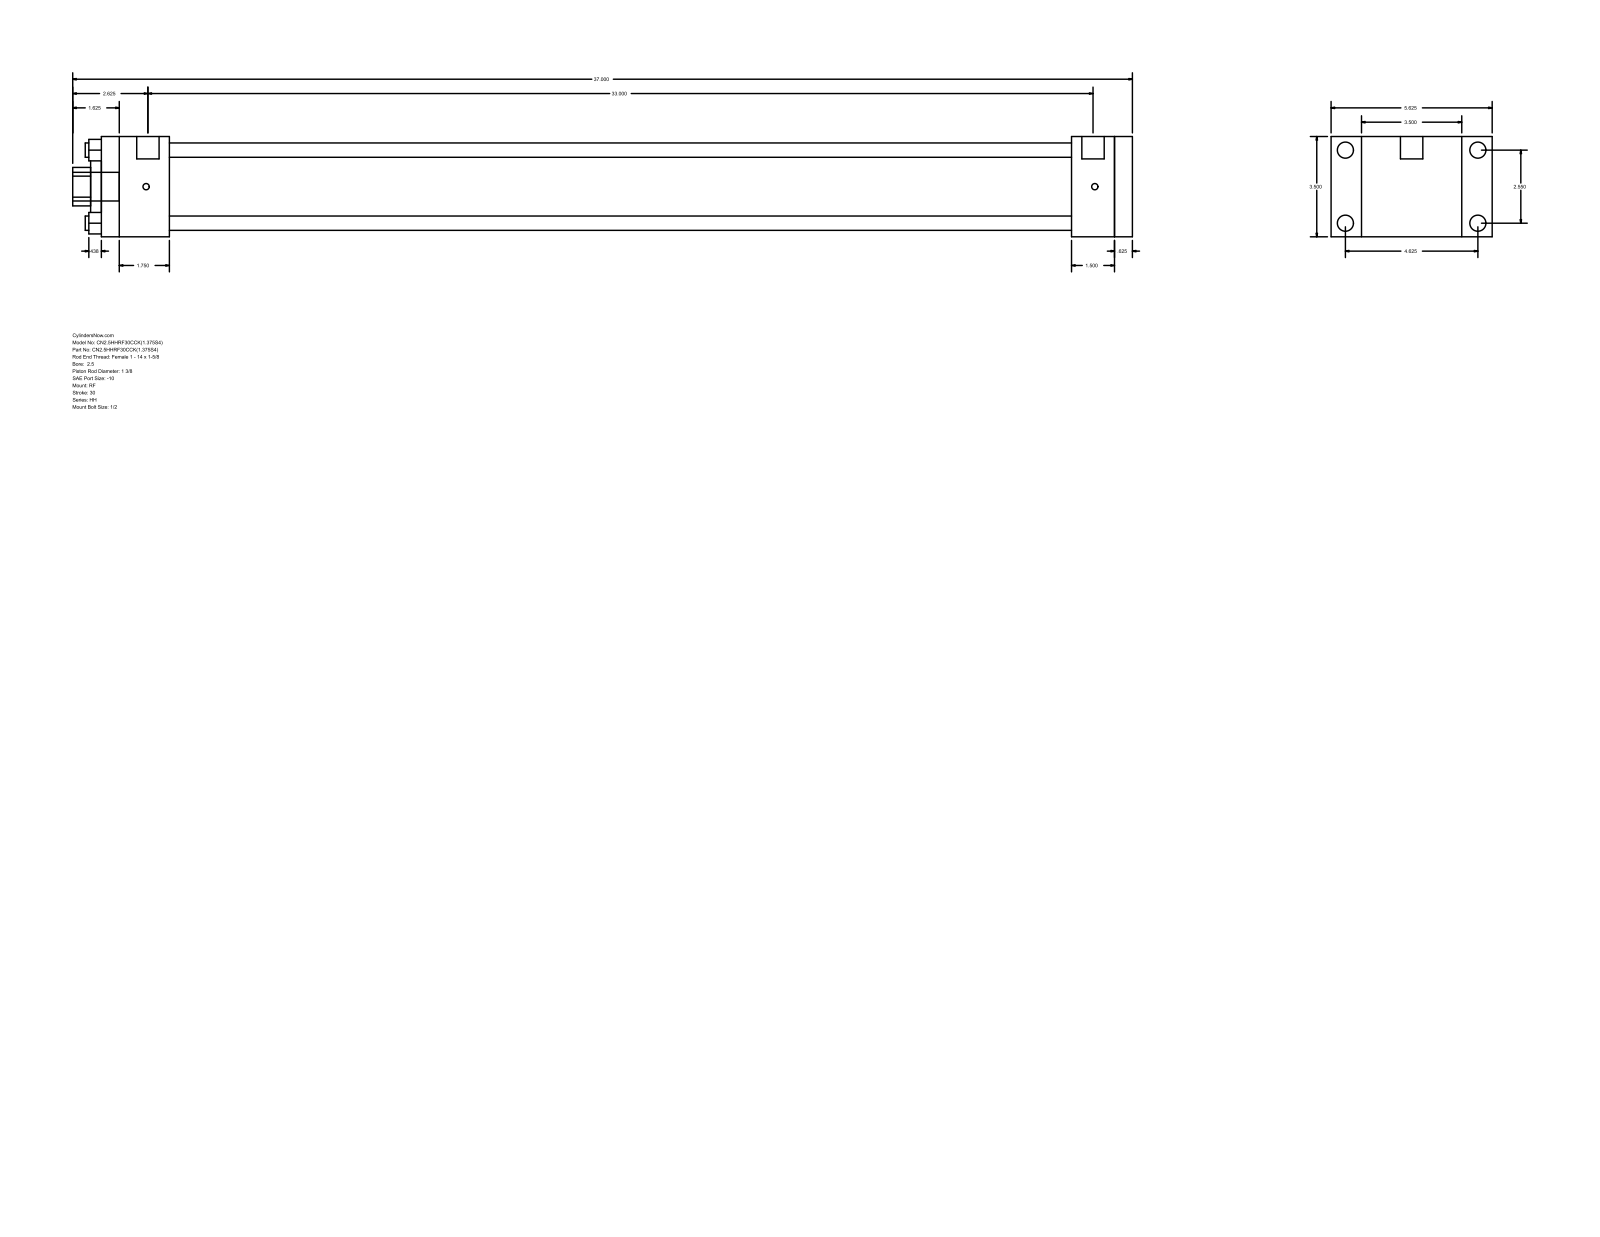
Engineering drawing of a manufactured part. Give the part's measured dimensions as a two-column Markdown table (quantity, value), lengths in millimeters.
| quantity | value |
| --- | --- |
| part name | HH_RF__0250_1.375 |
| STEP written by | GSSL Pune (CONFIG_CONTROL_DESIGN) |
| units | millimeters |
| bodies | 0 solids, 92 faces (64 planar, 28 cylindrical, 0 other) |
| overall size | 939.8 × 142.88 × 88.9 |
| round holes (diameter × count) | 12.7 × 4, 34.92 × 1, 50.8 × 1, 73.03 × 1 |
| round bosses / shafts (diameter × count) | 14.3 × 4, 5.56 × 4, 19.84 × 2, 25.4 × 1 |
| partial cylindrical surfaces (radius × count) | 17.06 × 1 |
| main face-to-face distances | 88.9, 914.4, 15.88, 898.52, 60.32, 838.2, 854.08, 860.43, 800.11, 38.09 |
| hole center spacings | 45.79, 64.76, 91.58 |
